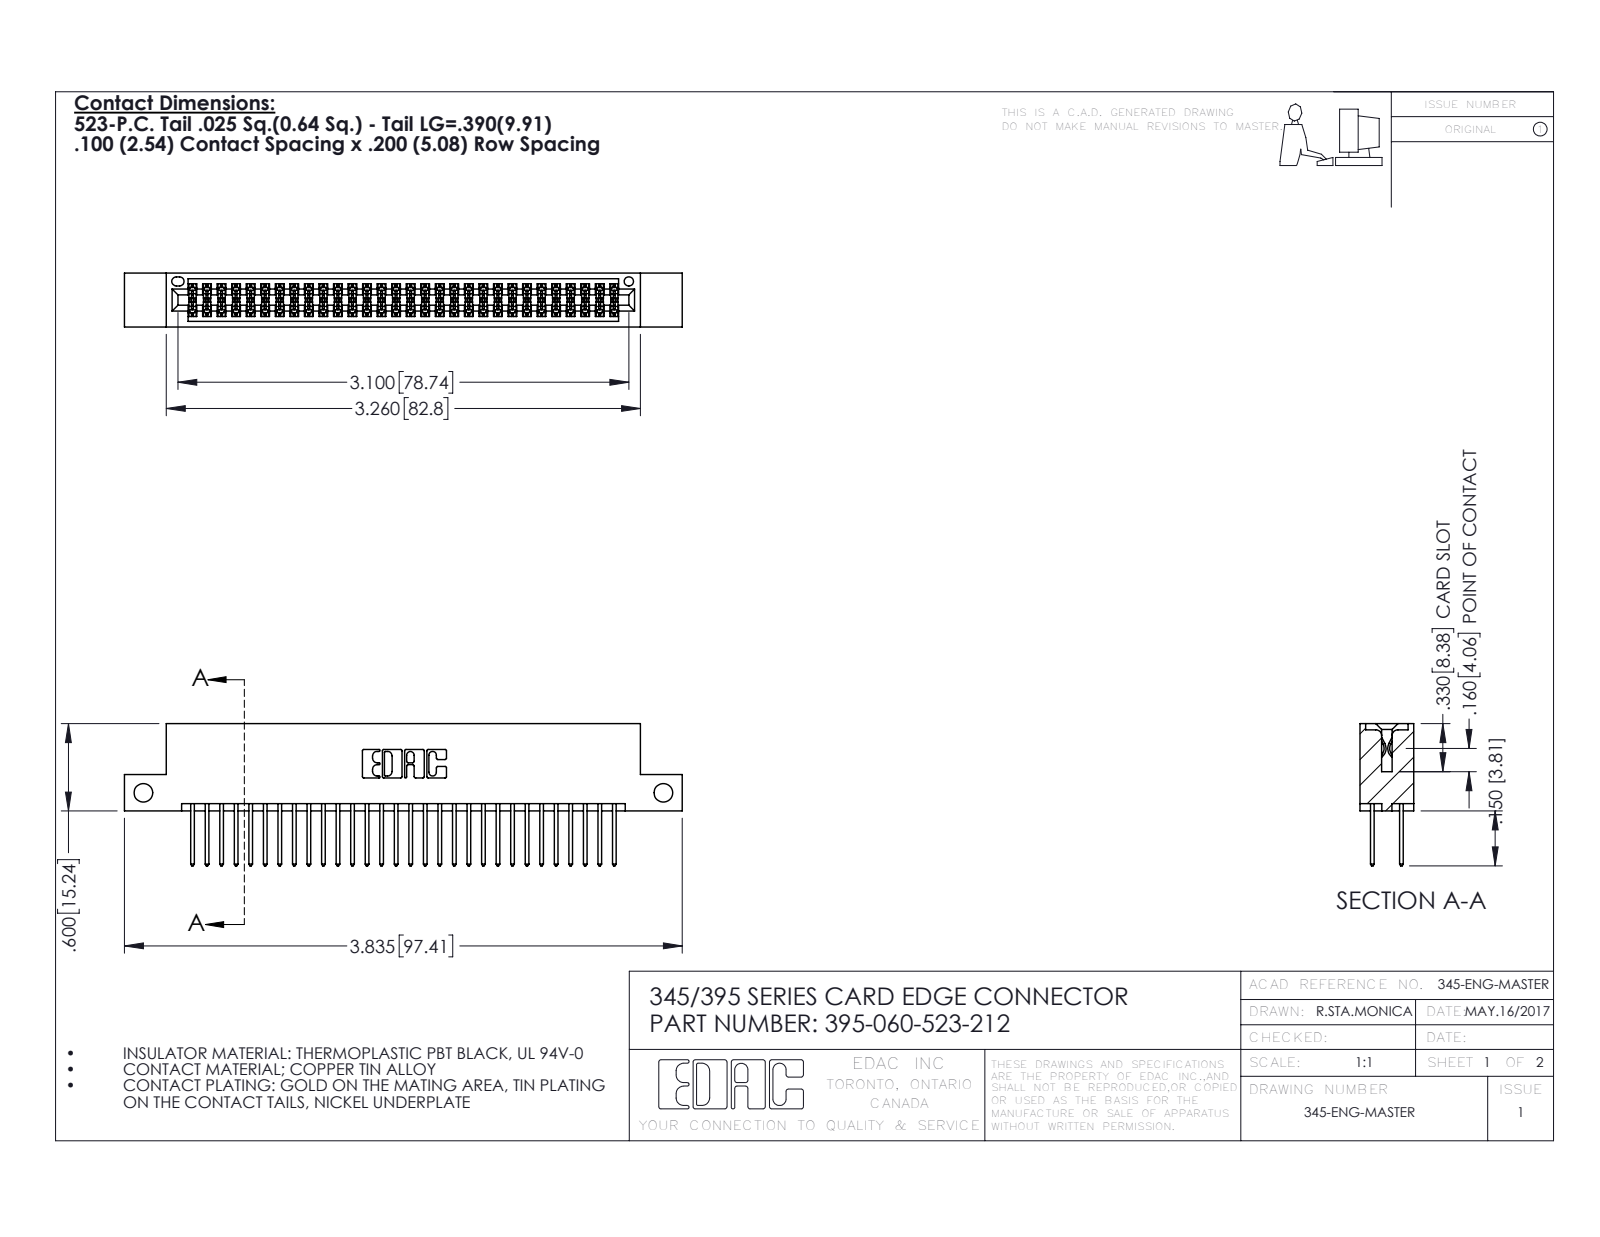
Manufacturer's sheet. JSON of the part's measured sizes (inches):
{"part_name": "395-060-523-212; 345 Part_Flush Mounting Lugs - Side Mount; 345-292-001_345-293-123", "step_written_by": "SolidWorks 2016 (CONFIG_CONTROL_DESIGN)", "units": "inches", "bodies": {"solids": 61, "faces": 3126, "planar": 2060, "cylindrical": 1066, "other": 0}, "overall_size": [3.835, 0.977, 0.37], "volume_in3": 0.573, "surface_area_in2": 21.79, "round_holes": [[0.128, 2], [0.064, 1]], "partial_cylinders_radius": [[0.006, 90], [0.01, 60], [0.01, 22], [0.007, 6], [0.031, 6], [0.026, 3], [0.014, 2], [0.019, 2]], "face_to_face_distances": [0.298, 0.072, 0.2, 0.098, 0.272, 0.025, 0.37, 0.225, 0.175, 0.149], "hole_center_spacings": [3.575]}
